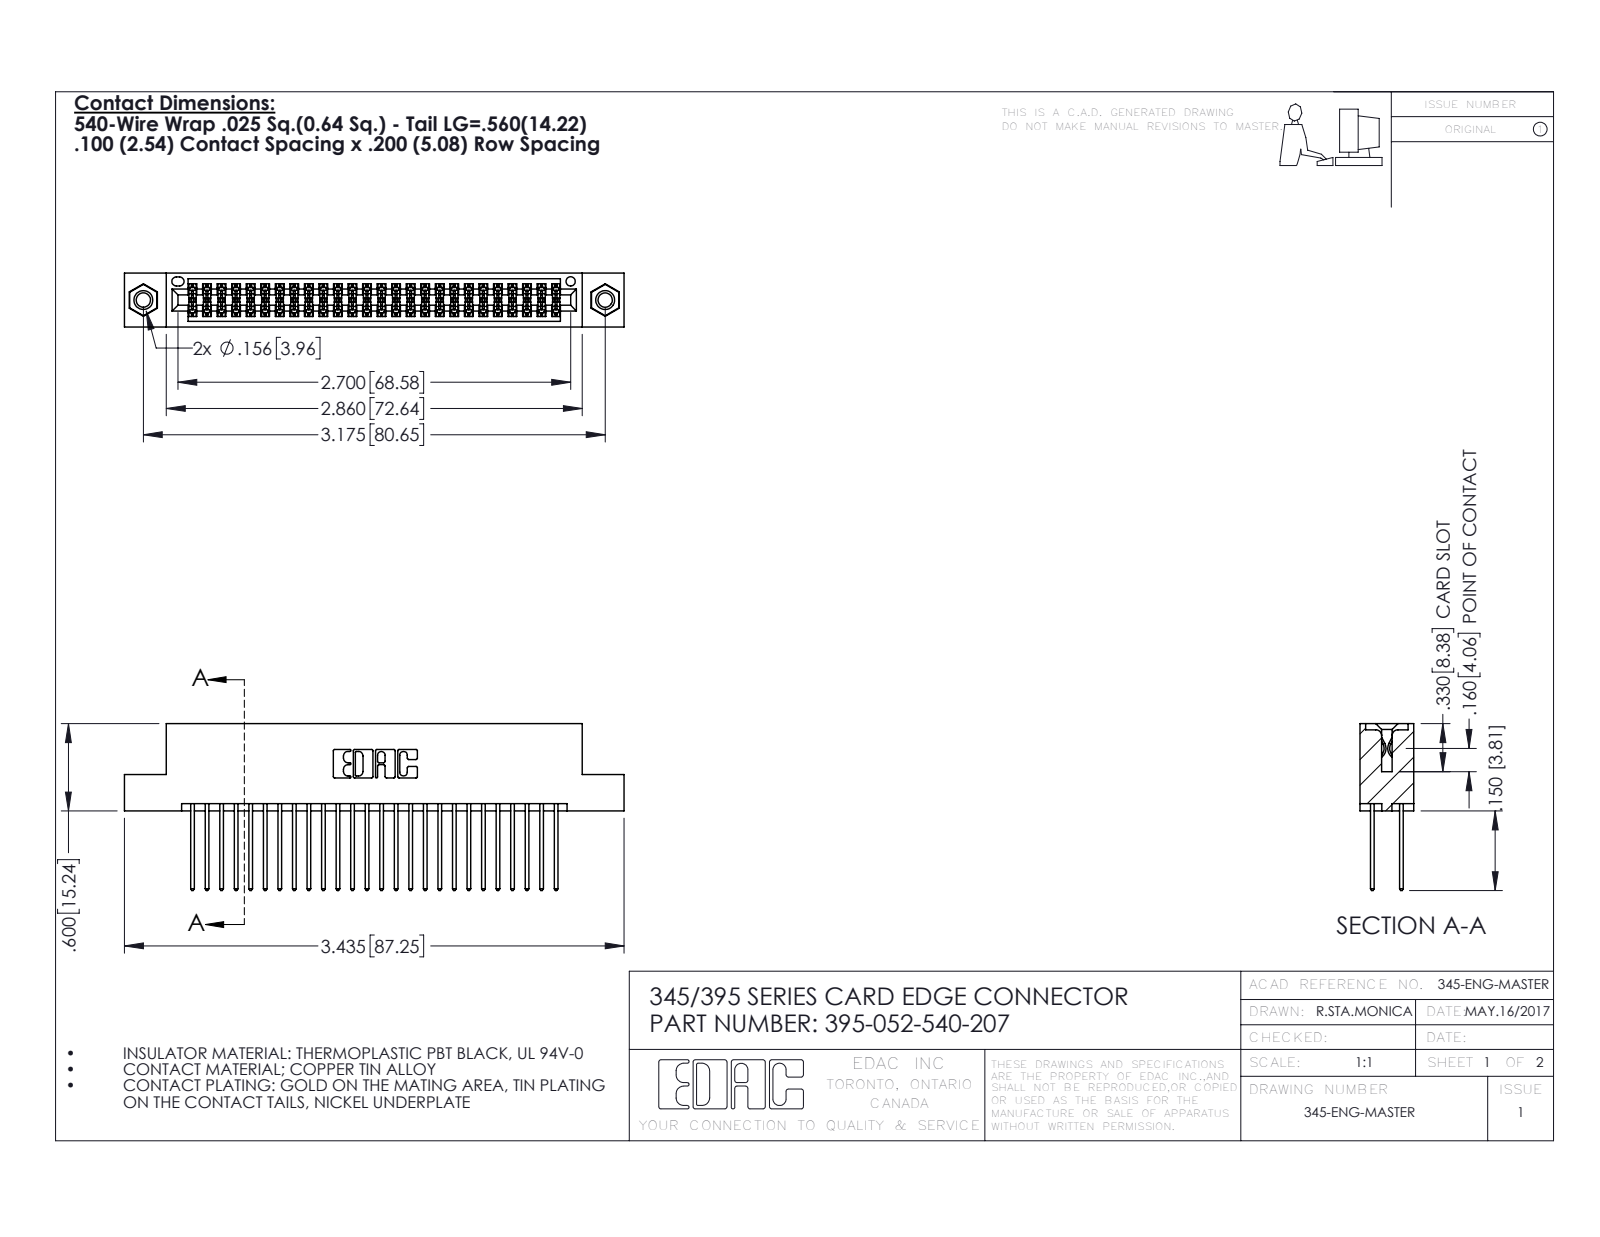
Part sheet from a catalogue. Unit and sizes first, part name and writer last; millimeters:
Units: millimetres
Overall size (bounding box): 87.2 × 29.1 × 9.4
Round holes (diameter × count): ⌀2.5 ×2, ⌀3.2 ×2, ⌀4 ×2, ⌀1.6 ×1
Round bosses / shafts (diameter × count): ⌀3.9 ×2
Partial cylindrical surfaces — rounded edges, fillets, slot ends (radius × count): R0.2 ×78, R0.3 ×52, R0.3 ×22, R0.2 ×6, R0.8 ×6, R0.7 ×3, R0.4 ×2, R0.5 ×2
Main face-to-face distances: 1.8, 7.6, 5.1, 2.5, 6.9, 0.6, 9.4, 5.7, 4.4, 3.8
Hole centre spacings: 6.9, 74.7, 80.6
Volume: 8 500 mm³ · Surface area: 13 210 mm²
Bodies: 55 solids, 2786 faces (1828 planar, 942 cylindrical, 16 other)
Part name (STEP PRODUCT): 395-052-540-207; 345 Part_Flush Mounting Lugs - 0.156 Dia-TI; 345-250-001_345-250-005-103; 345-292-001_345-293-140
STEP written by: SolidWorks 2016 (CONFIG_CONTROL_DESIGN)
